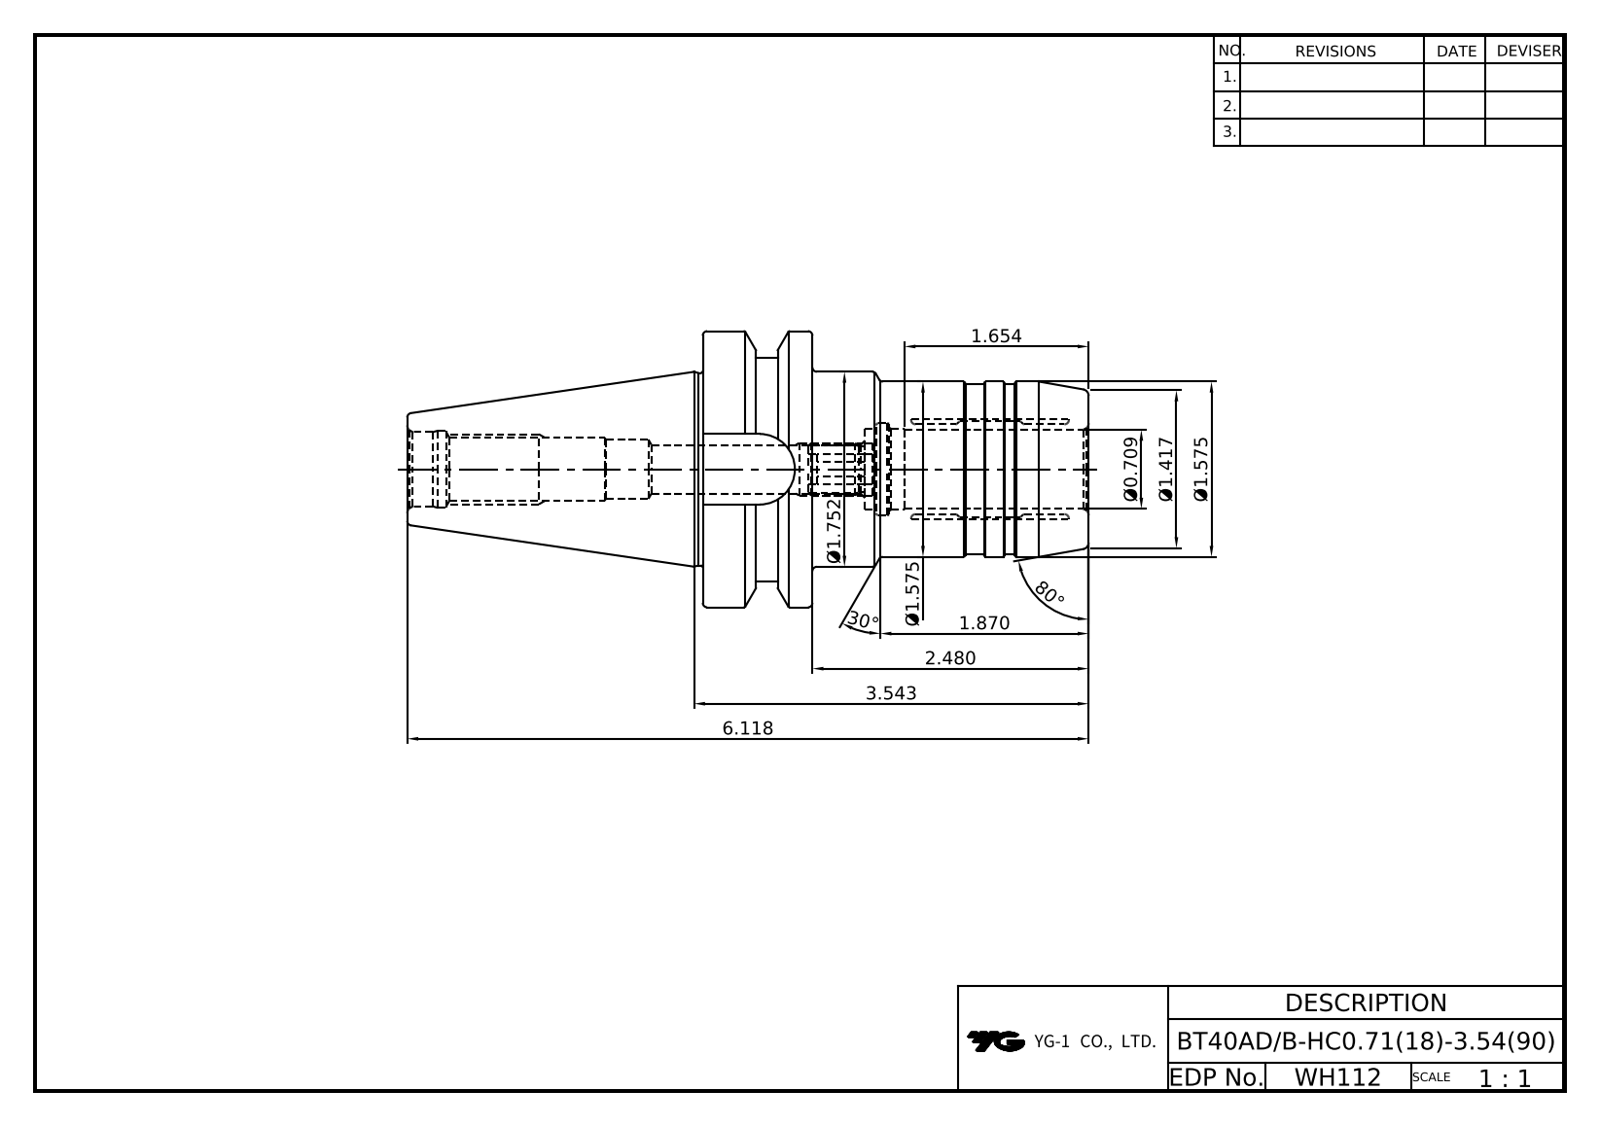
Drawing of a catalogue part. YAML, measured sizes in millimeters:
part_name: "LO-BT40ADB-HC18-90"
step_written_by: "Autodesk Inventor 2022 (AUTOMOTIVE_DESIGN)"
units: millimeters
bodies: {solids: 1, faces: 88, planar: 21, cylindrical: 33, other: 34}
overall_size: [155.4, 63, 63]
volume: 188096
surface_area: 34103
round_holes:
  - {diameter: 3.24, count: 4}
  - {diameter: 4, count: 4}
  - {diameter: 10.92, count: 1}
  - {diameter: 13.5, count: 1}
  - {diameter: 13.84, count: 1}
  - {diameter: 17, count: 1}
  - {diameter: 17.6, count: 1}
  - {diameter: 18, count: 1}
  - {diameter: 18.4, count: 1}
round_bosses_or_shafts:
  - {diameter: 63, count: 1}
  - {diameter: 51, count: 1}
  - {diameter: 44.5, count: 1}
  - {diameter: 44, count: 1}
  - {diameter: 40, count: 1}
  - {diameter: 39, count: 1}
partial_cylinders:
  - {radius: 8.05, count: 1}
face_to_face_distances: [25, 88, 63, 45.2, 17.1, 7.9, 70.9, 12.1, 5, 12.9]
